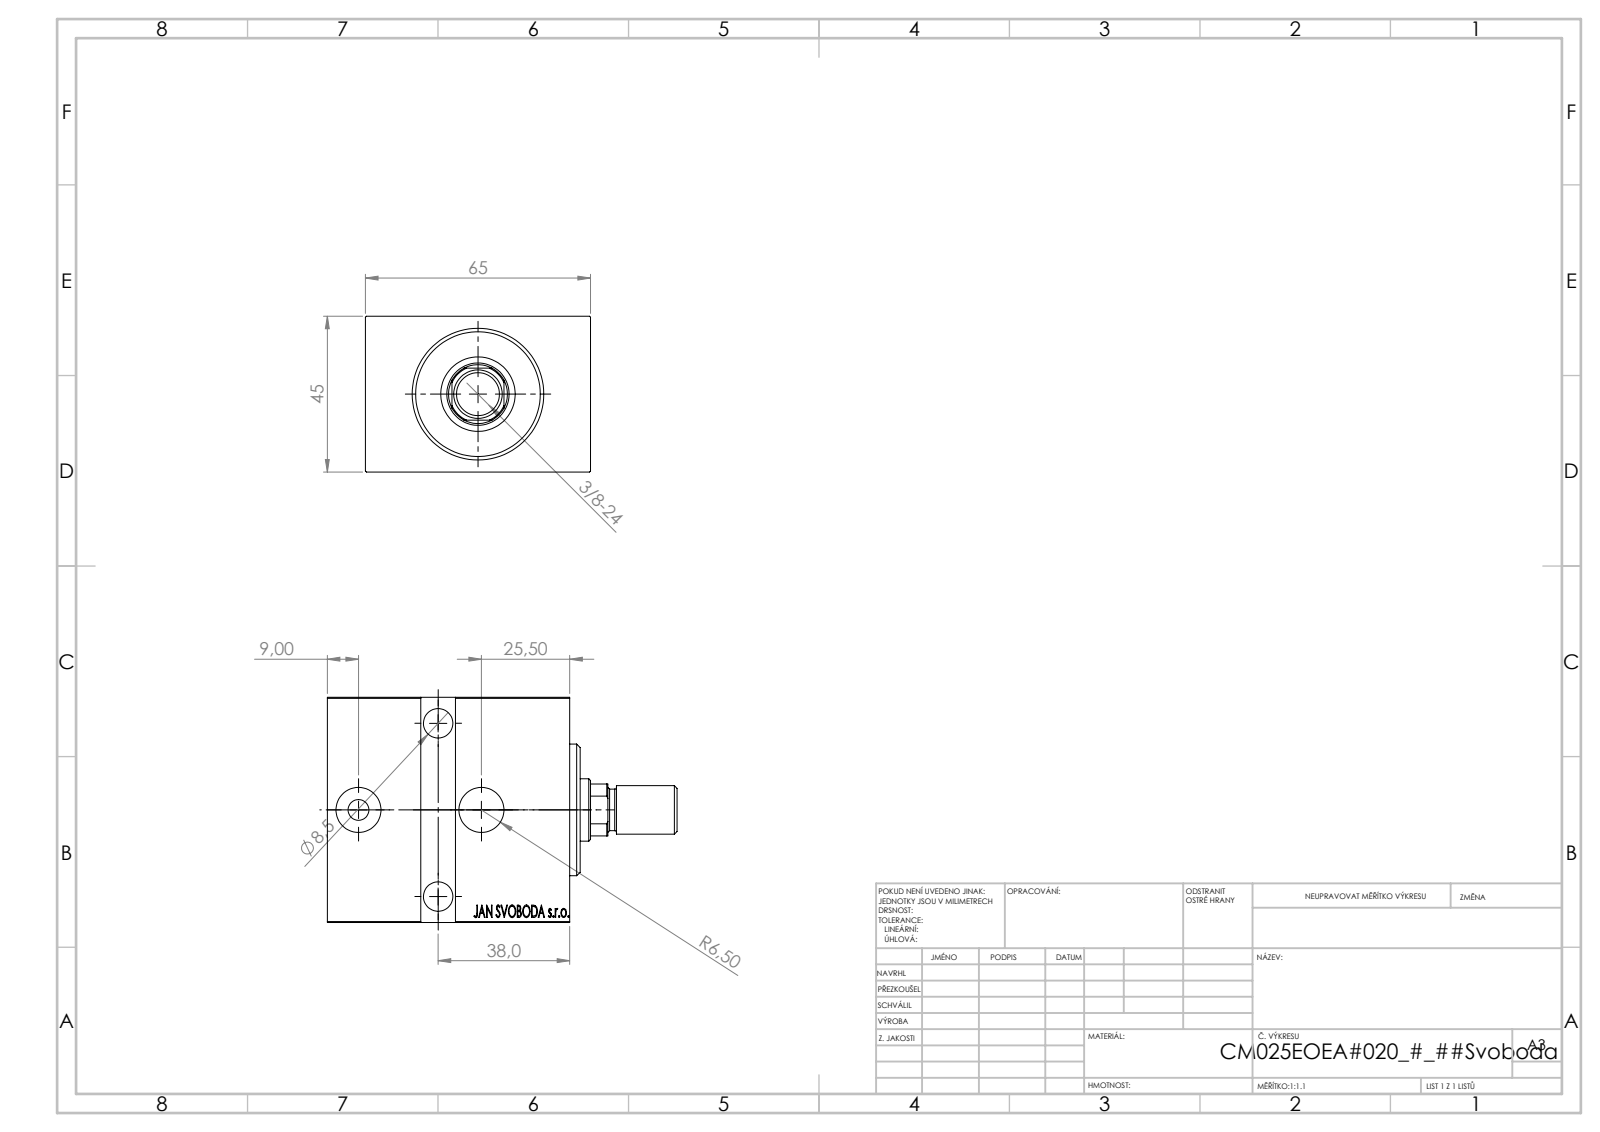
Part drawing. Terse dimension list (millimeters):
name: V450CM_E_VCP; V450CM_MALE_METRIC; V450CM_E_Body; V450CM_VC_B
written by: SolidWorks 2019 (CONFIG_CONTROL_DESIGN)
unit: mm
bodies: 4 solids, 852 faces (410 planar, 42 cylindrical, 400 other)
size: 101 × 65 × 45
volume: 198 016 mm³; area: 40 206 mm²
holes: 3× ⌀8.5, 2× ⌀13, 2× ⌀13.5, 1× ⌀18, 1× ⌀21.5, 1× ⌀25, 1× ⌀35
bosses: 1× ⌀38, 1× ⌀27, 1× ⌀14, 1× ⌀12, 1× ⌀6
rounds: 1× R8.5
face distances: 65, 45, 70, 8, 64, 3, 6, 5, 59, 43
hole spacings: 27.95, 33.97, 35.5, 50
